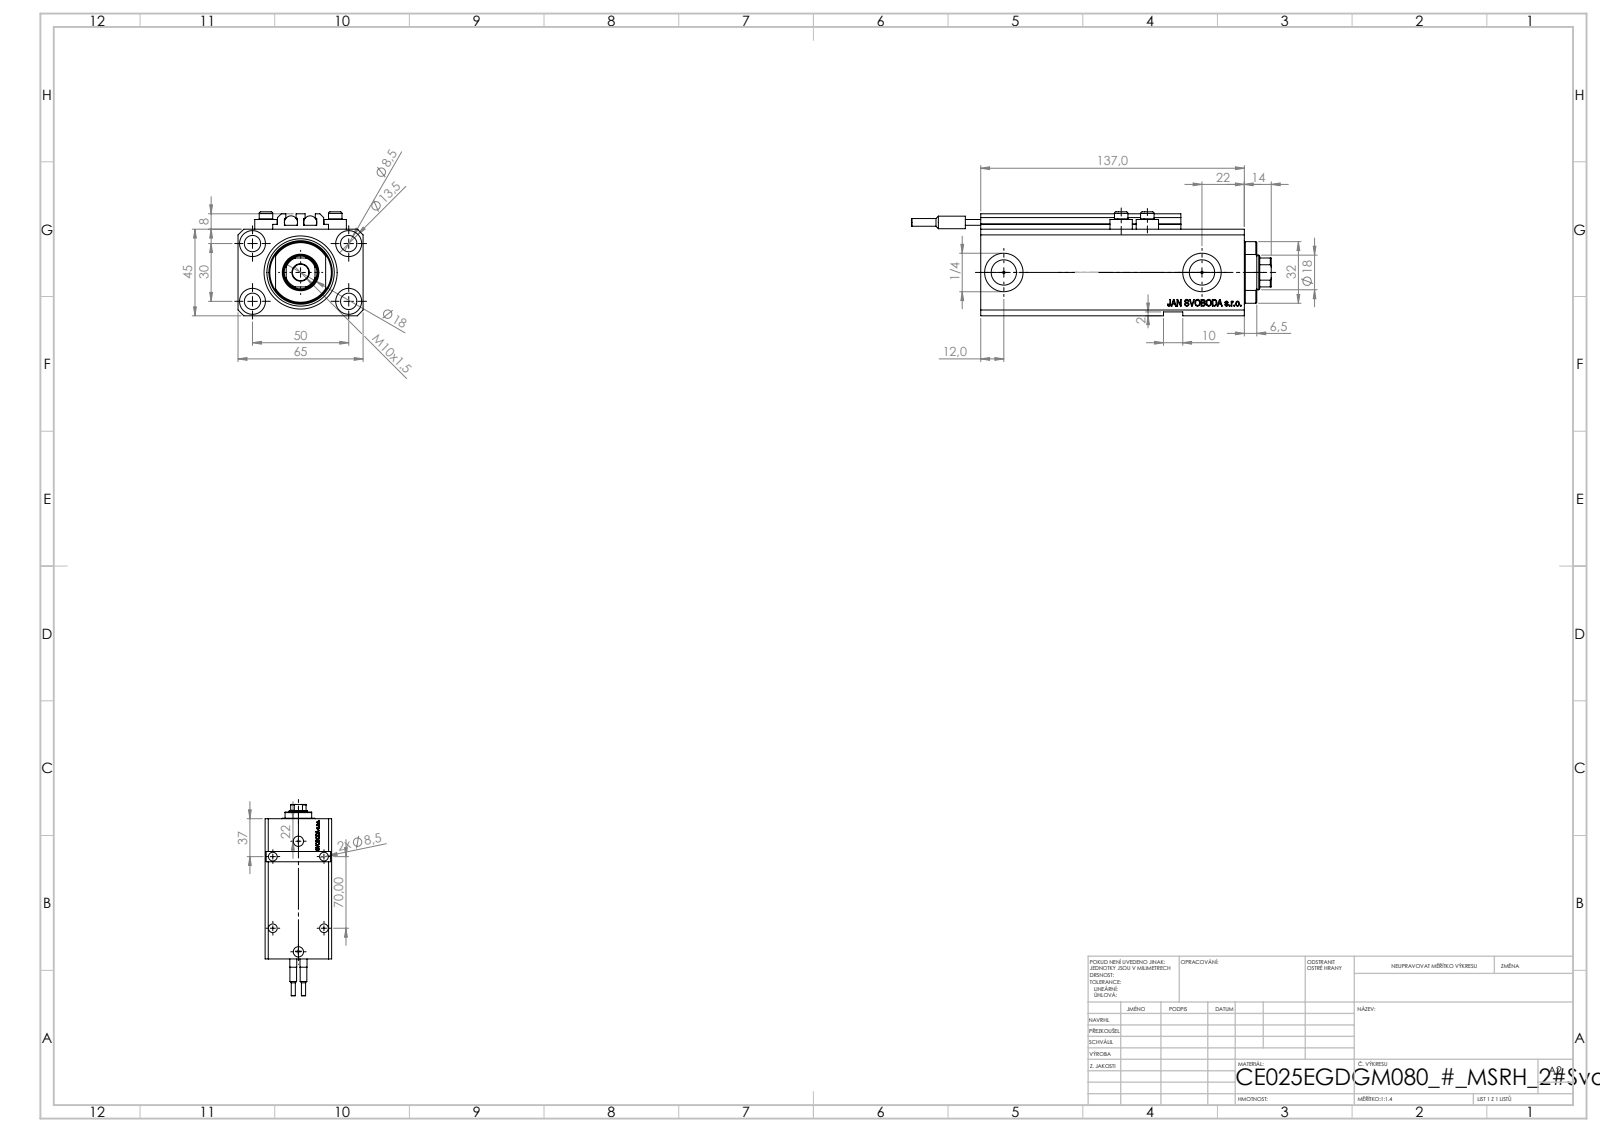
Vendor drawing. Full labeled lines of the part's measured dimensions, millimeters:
Part name (STEP PRODUCT): SWITCH_V250CE; V250CE_VC_E; V250CE_E_Body; ALLEN BOLT V250CE (+1 more)
STEP written by: SolidWorks 2019 (CONFIG_CONTROL_DESIGN)
Units: millimetres
Bodies: 10 solids, 1155 faces (547 planar, 170 cylindrical, 438 other)
Overall size (bounding box): 187 × 65 × 54
Volume: 350 450 mm³ · Surface area: 97 433 mm²
Round holes (diameter × count): ⌀8.5 ×9, ⌀1.25 ×4, ⌀4 ×4, ⌀13.5 ×4, ⌀10 ×2, ⌀13.16 ×2, ⌀20 ×2, ⌀18 ×1, ⌀25 ×1, ⌀38 ×1
Round bosses / shafts (diameter × count): ⌀11.6 ×4, ⌀7 ×4, ⌀6.8 ×2, ⌀6.5 ×2, ⌀4 ×2
Partial cylindrical surfaces — rounded edges, fillets, slot ends (radius × count): R0.2 ×10, R8.5 ×1, R16 ×1
Main face-to-face distances: 45, 65, 47, 2, 2.5, 10, 3, 123, 14, 20.4
Hole centre spacings: 29.15, 50, 13.6, 15.12, 27.89, 30, 33.61, 33.62
